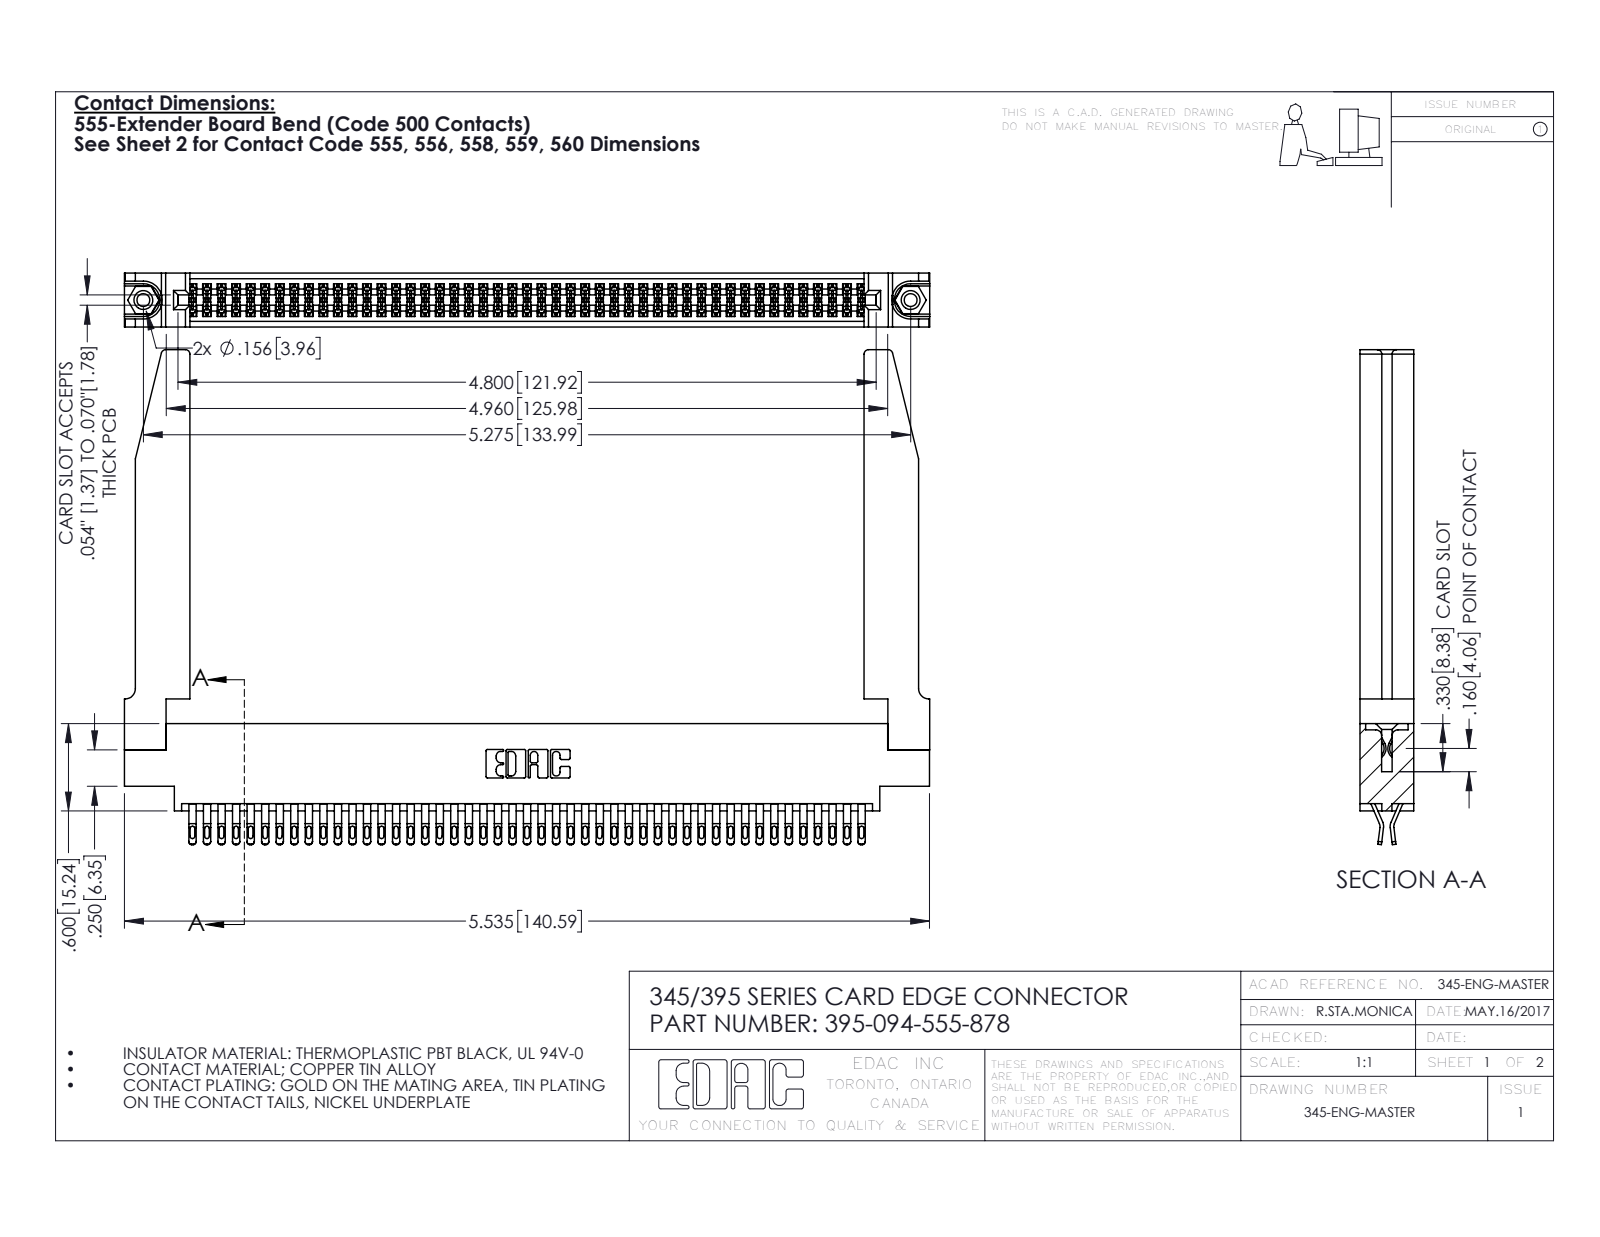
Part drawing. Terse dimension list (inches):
name: 345-250-001_345-250-001-102; 395-094-555-878; 345-220-078_345-220-078; 345-292-001_555 Tail (+1 more)
written by: SolidWorks 2016 (CONFIG_CONTROL_DESIGN)
unit: in
bodies: 99 solids, 5628 faces (3140 planar, 2436 cylindrical, 52 other)
size: 5.536 × 3.402 × 0.37
volume: 1.32 in³; area: 44.21 in²
holes: 2× ⌀0.089, 2× ⌀0.125, 2× ⌀0.156, 1× ⌀0.064
bosses: 2× ⌀0.155
rounds: 235× R0.016, 188× R0.02, 141× R0.006, 22× R0.01, 8× R0.03, 6× R0.007, 6× R0.031, 3× R0.026
face distances: 0.37, 0.072, 0.298, 0.025, 0.098, 0.272, 0.2, 0.225, 0.175, 0.148
hole spacings: 0.27, 5.039, 5.275
